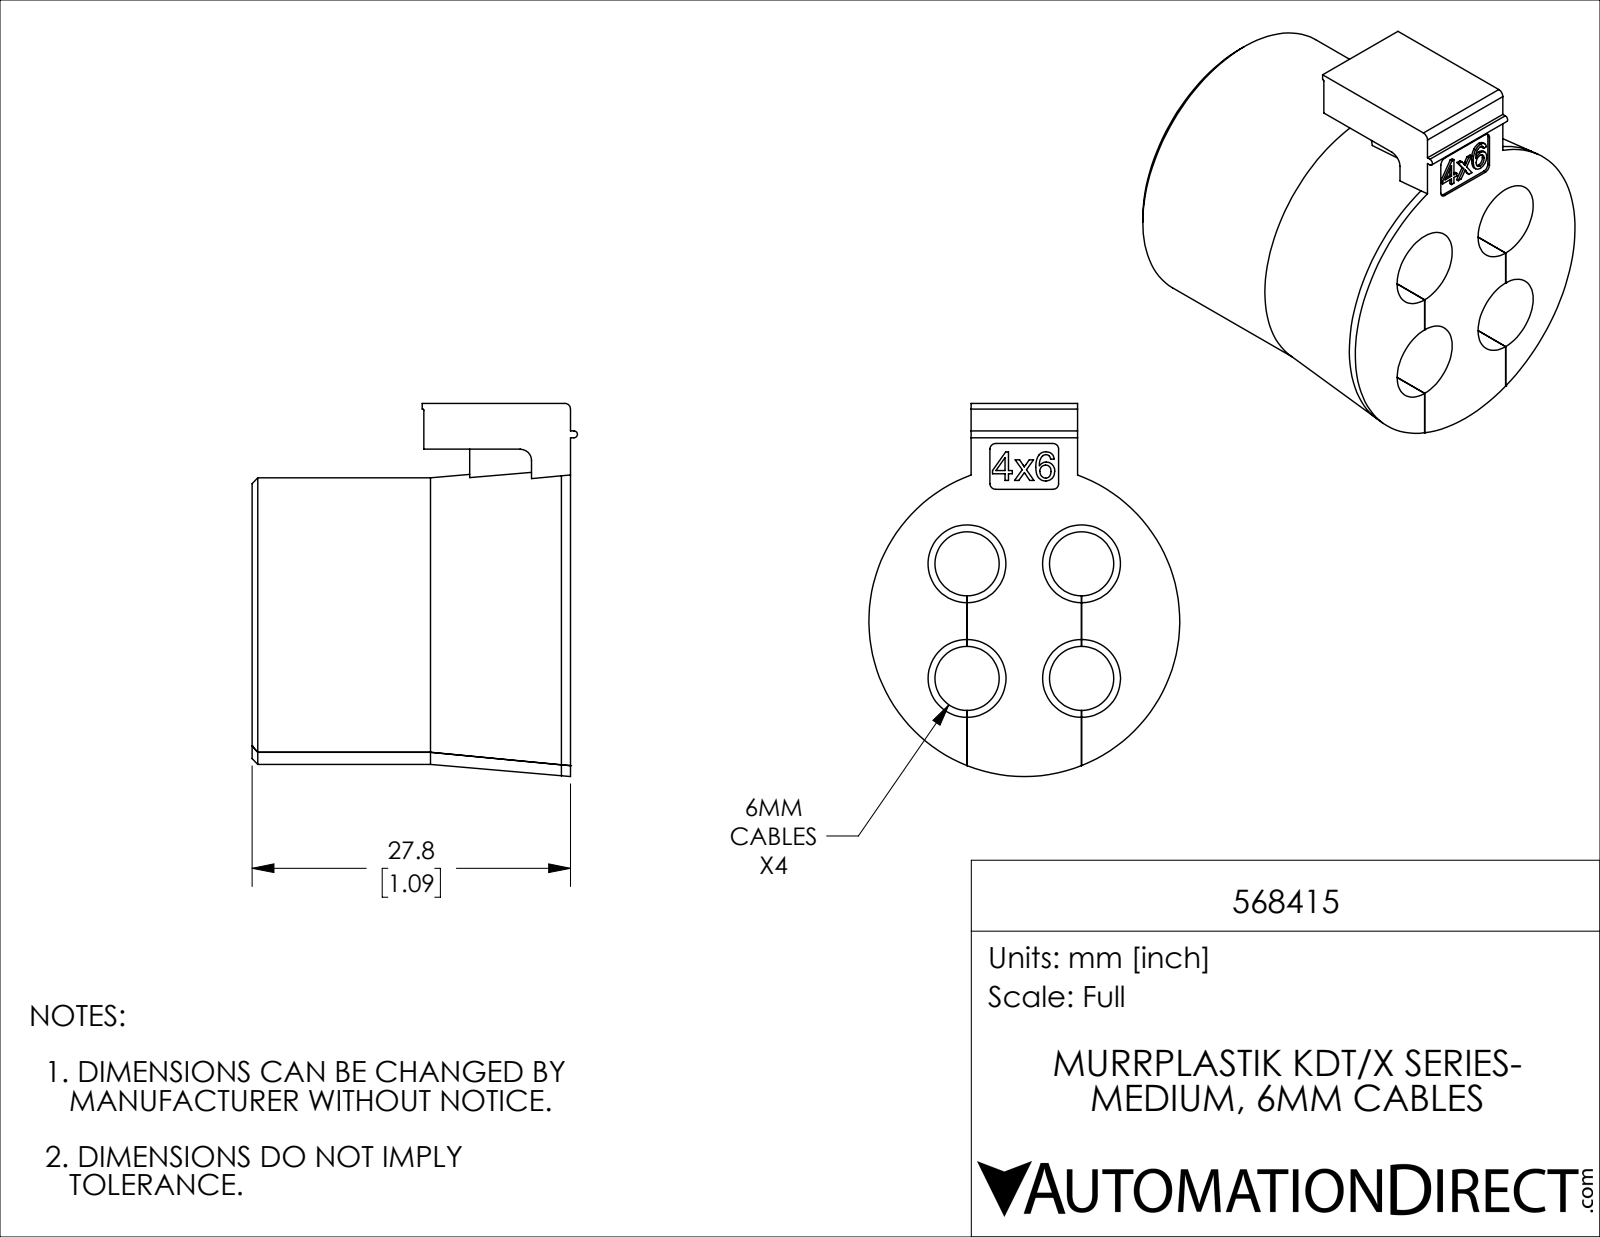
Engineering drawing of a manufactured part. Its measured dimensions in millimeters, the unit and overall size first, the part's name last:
Units: millimetres
Overall size (bounding box): 32.6 × 28.4 × 27.2
Round holes (diameter × count): ⌀5.6 ×4, ⌀6.8 ×4
Round bosses / shafts (diameter × count): ⌀25 ×1
Partial cylindrical surfaces — rounded edges, fillets, slot ends (radius × count): R0.5 ×5, R0.1 ×1, R0.3 ×1, R1 ×1
Main face-to-face distances: 10, 27.8, 10, 10, 0.3, 0.4, 9.7, 9.7, 4, 9.3
Hole centre spacings: 10, 14.1
Volume: 10 700 mm³ · Surface area: 6 516 mm²
Bodies: 1 solid, 164 faces (63 planar, 50 cylindrical, 51 other)
Part name (STEP PRODUCT): 568415
STEP written by: SolidWorks 2019 (CONFIG_CONTROL_DESIGN)
